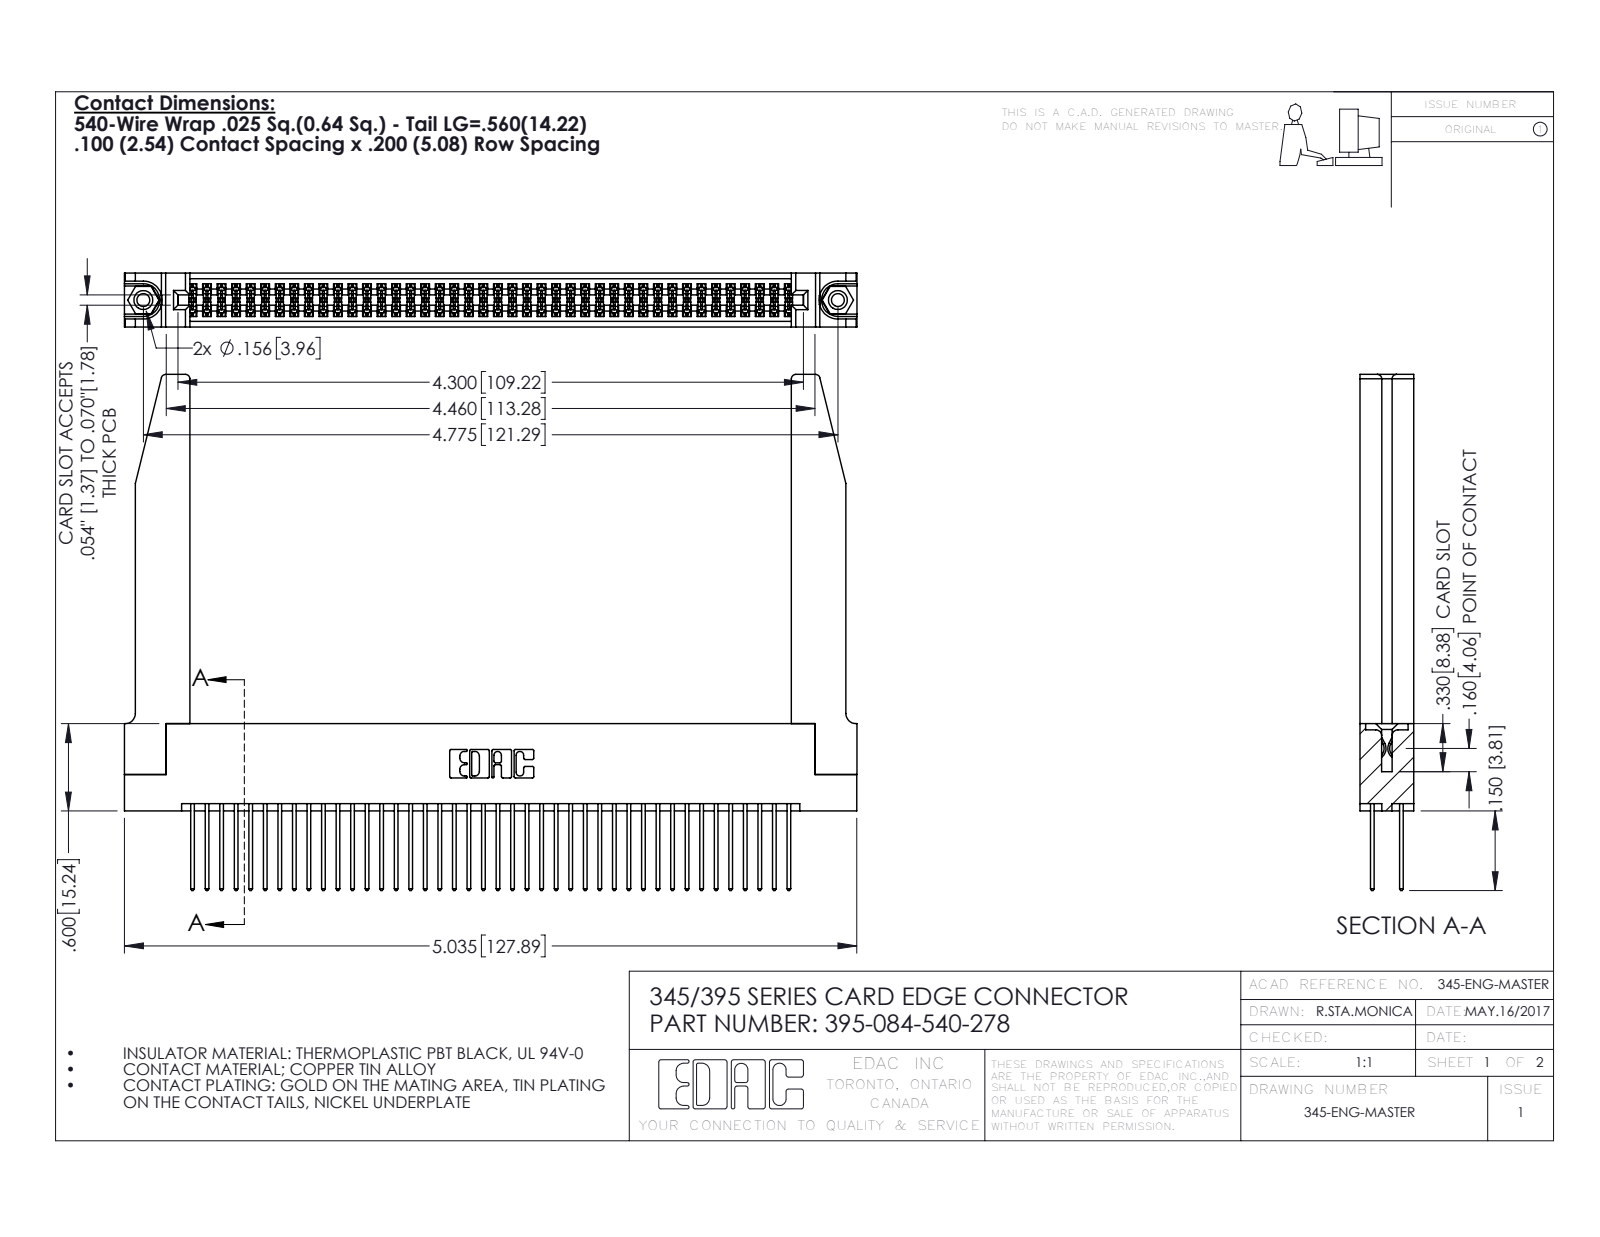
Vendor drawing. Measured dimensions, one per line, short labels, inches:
name: 345 Part_Flush Mounting Lugs - 0.156 Dia-TH; 345-292-001_345-293-140; 345-220-078_345-220-078; 345-250-001_345-250-001-102 (+1 more)
written by: SolidWorks 2016 (CONFIG_CONTROL_DESIGN)
unit: in
bodies: 89 solids, 4560 faces (2994 planar, 1514 cylindrical, 52 other)
size: 5.036 × 3.547 × 0.37
volume: 1.252 in³; area: 42.09 in²
holes: 2× ⌀0.089, 2× ⌀0.125, 2× ⌀0.156, 1× ⌀0.064
bosses: 2× ⌀0.155
rounds: 126× R0.006, 84× R0.01, 22× R0.01, 8× R0.03, 6× R0.007, 6× R0.031, 3× R0.026, 2× R0.014
face distances: 0.072, 0.298, 0.37, 0.2, 0.098, 0.272, 0.025, 0.225, 0.175, 0.148
hole spacings: 0.27, 4.539, 4.775
